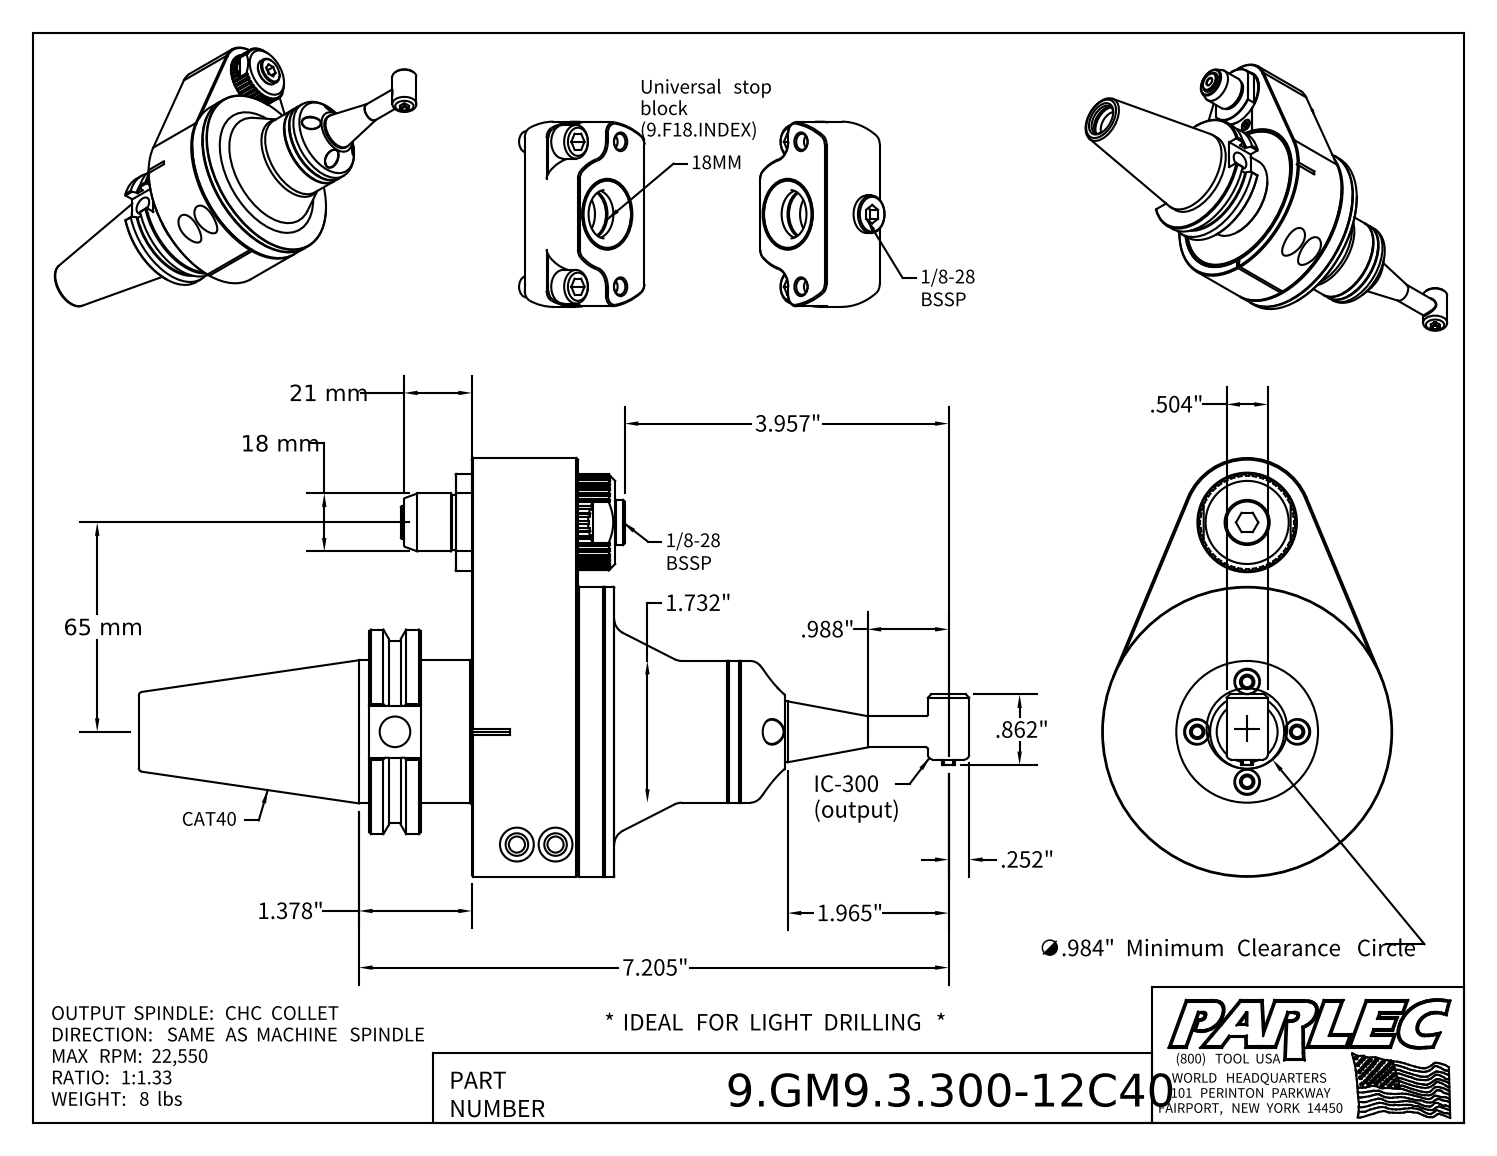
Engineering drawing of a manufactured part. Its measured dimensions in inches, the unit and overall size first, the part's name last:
Units: inches
Overall size (bounding box): 10.15 × 5.118 × 3.543
Round holes (diameter × count): ⌀0.165 ×6, ⌀0.13 ×5, ⌀0.177 ×4, ⌀0.197 ×4, ⌀0.295 ×4, ⌀0.157 ×2, ⌀0.236 ×2, ⌀0.276 ×2, ⌀0.413 ×2, ⌀0.551 ×2, ⌀0.709 ×2, ⌀0.256 ×1
Round bosses / shafts (diameter × count): ⌀1.181 ×2, ⌀0.669 ×2, ⌀0.394 ×2, ⌀3.543 ×1, ⌀3.228 ×1, ⌀3.071 ×1, ⌀2.5 ×1, ⌀2.219 ×1
Partial cylindrical surfaces — rounded edges, fillets, slot ends (radius × count): R0.033 ×2, R0.085 ×2, R0.079 ×1, R0.093 ×1, R0.098 ×1, R0.587 ×1, R0.596 ×1, R0.787 ×1
Main face-to-face distances: 1.299, 0.118, 1.181, 0.197, 0.315, 0.626, 1.74, 1.622, 0.441, 0.984
Hole centre spacings: 1.476, 1.598, 0.61, 0.764, 0.863, 0.866, 0.996, 1.285
Volume: 27.87 in³ · Surface area: 182.9 in²
Bodies: 21 solids, 645 faces (293 planar, 167 cylindrical, 185 other)
Part name (STEP PRODUCT): 9.GM9.3.300-12C40; 9_GA1_446_1 (Classic, Type 1, Cat40, 65mm); GM90300-000MC
STEP written by: Autodesk Inventor 2022 (AUTOMOTIVE_DESIGN)
